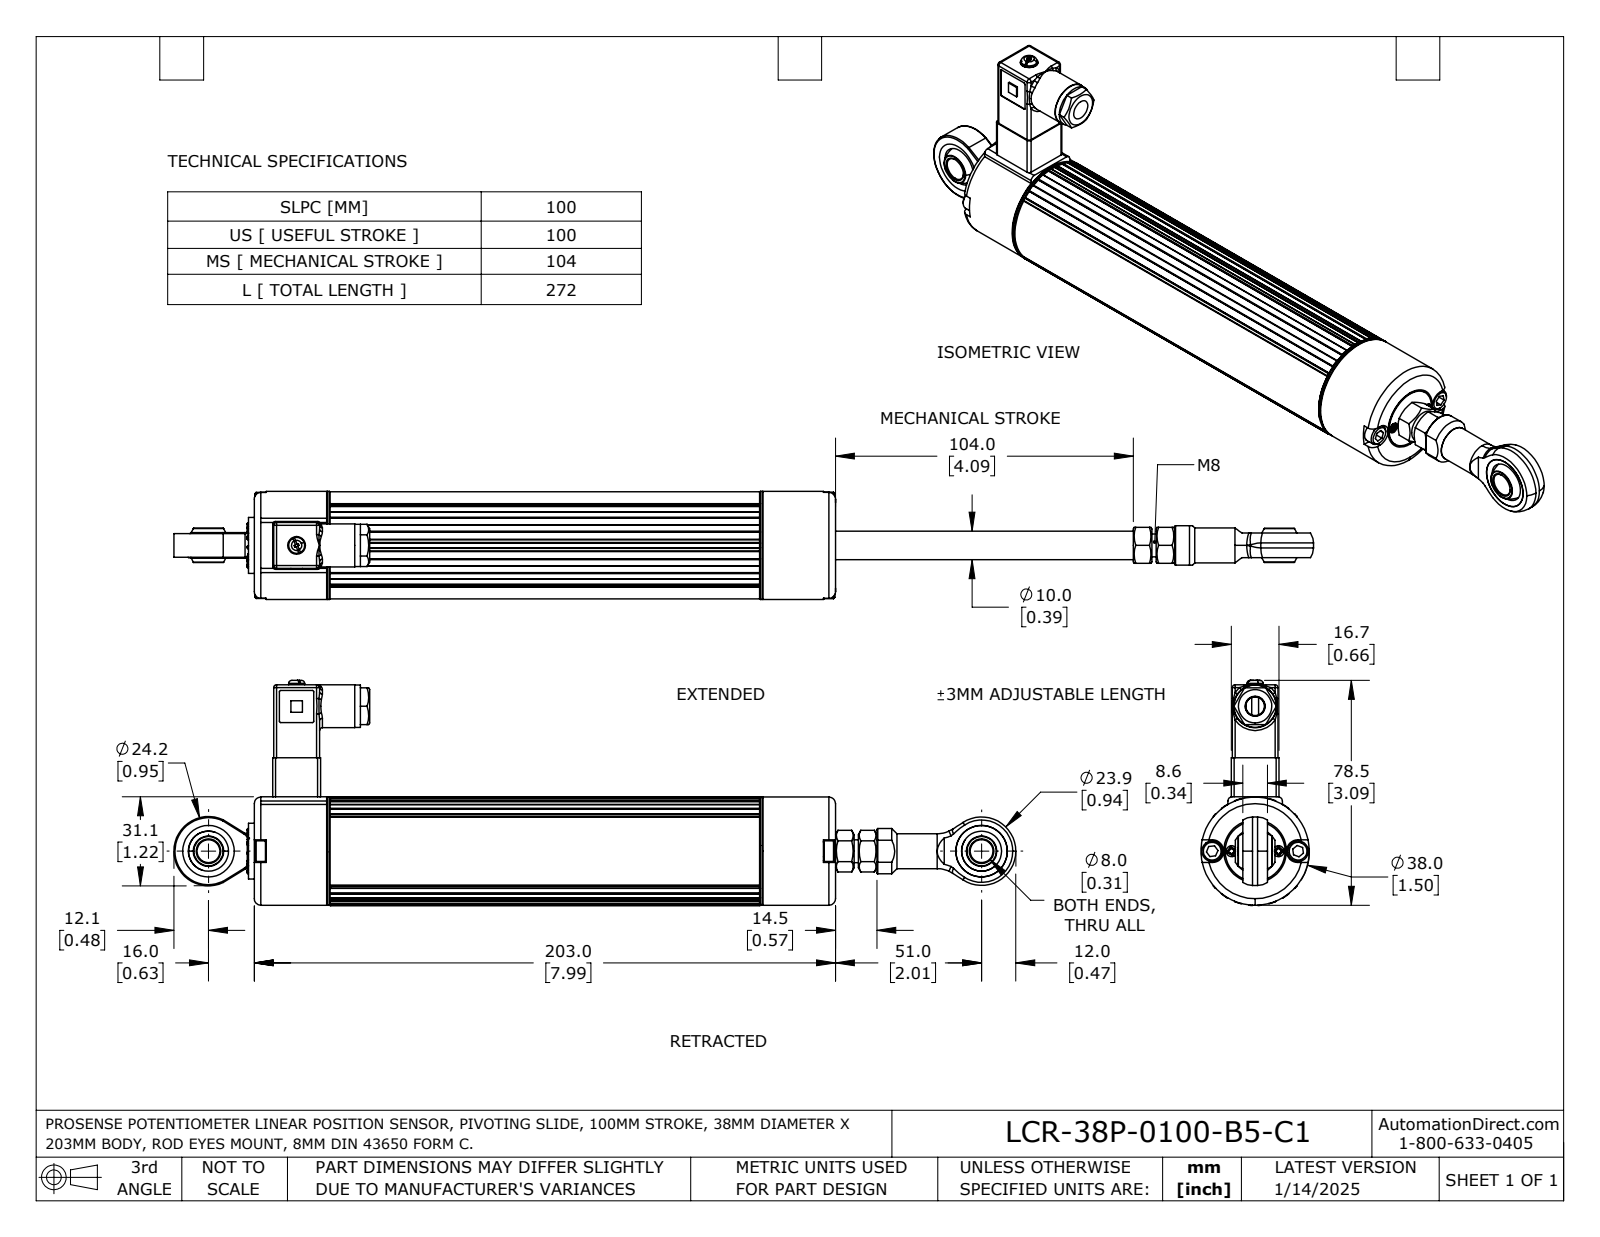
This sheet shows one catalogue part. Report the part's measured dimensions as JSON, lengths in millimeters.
{"part_name": "LCR-38P-0100-B5-C1", "step_written_by": "SolidWorks 2023 (AUTOMOTIVE_DESIGN)", "units": "millimeters", "bodies": {"solids": 11, "faces": 657, "planar": 295, "cylindrical": 210, "other": 152}, "overall_size": [294.1, 78.6, 37.8], "volume_mm3": 245800, "surface_area_mm2": 55310, "round_holes": [[2.6, 6], [2.3, 4], [8, 3], [14, 3], [2.4, 2], [2.5, 2], [2.8, 2], [3.4, 2], [3.9, 2], [4.2, 2], [2, 1], [3, 1]], "round_bosses_or_shafts": [[1.6, 6], [7.2, 4], [3.8, 4], [12.2, 2], [2, 2], [37.8, 1], [20.9, 1], [19.5, 1]], "partial_cylinders_radius": [[0.2, 32], [1, 20], [0.5, 12], [0.4, 6], [0.3, 2], [1.5, 2], [2.1, 2], [2.5, 2]], "face_to_face_distances": [150, 26.5, 176.5, 0.8, 1.1, 15.5, 15.2, 0.4, 16.4, 3.5], "hole_center_spacings": [16.1, 1.9, 16.1, 6.7, 6.8, 7.2, 8.2, 10]}
